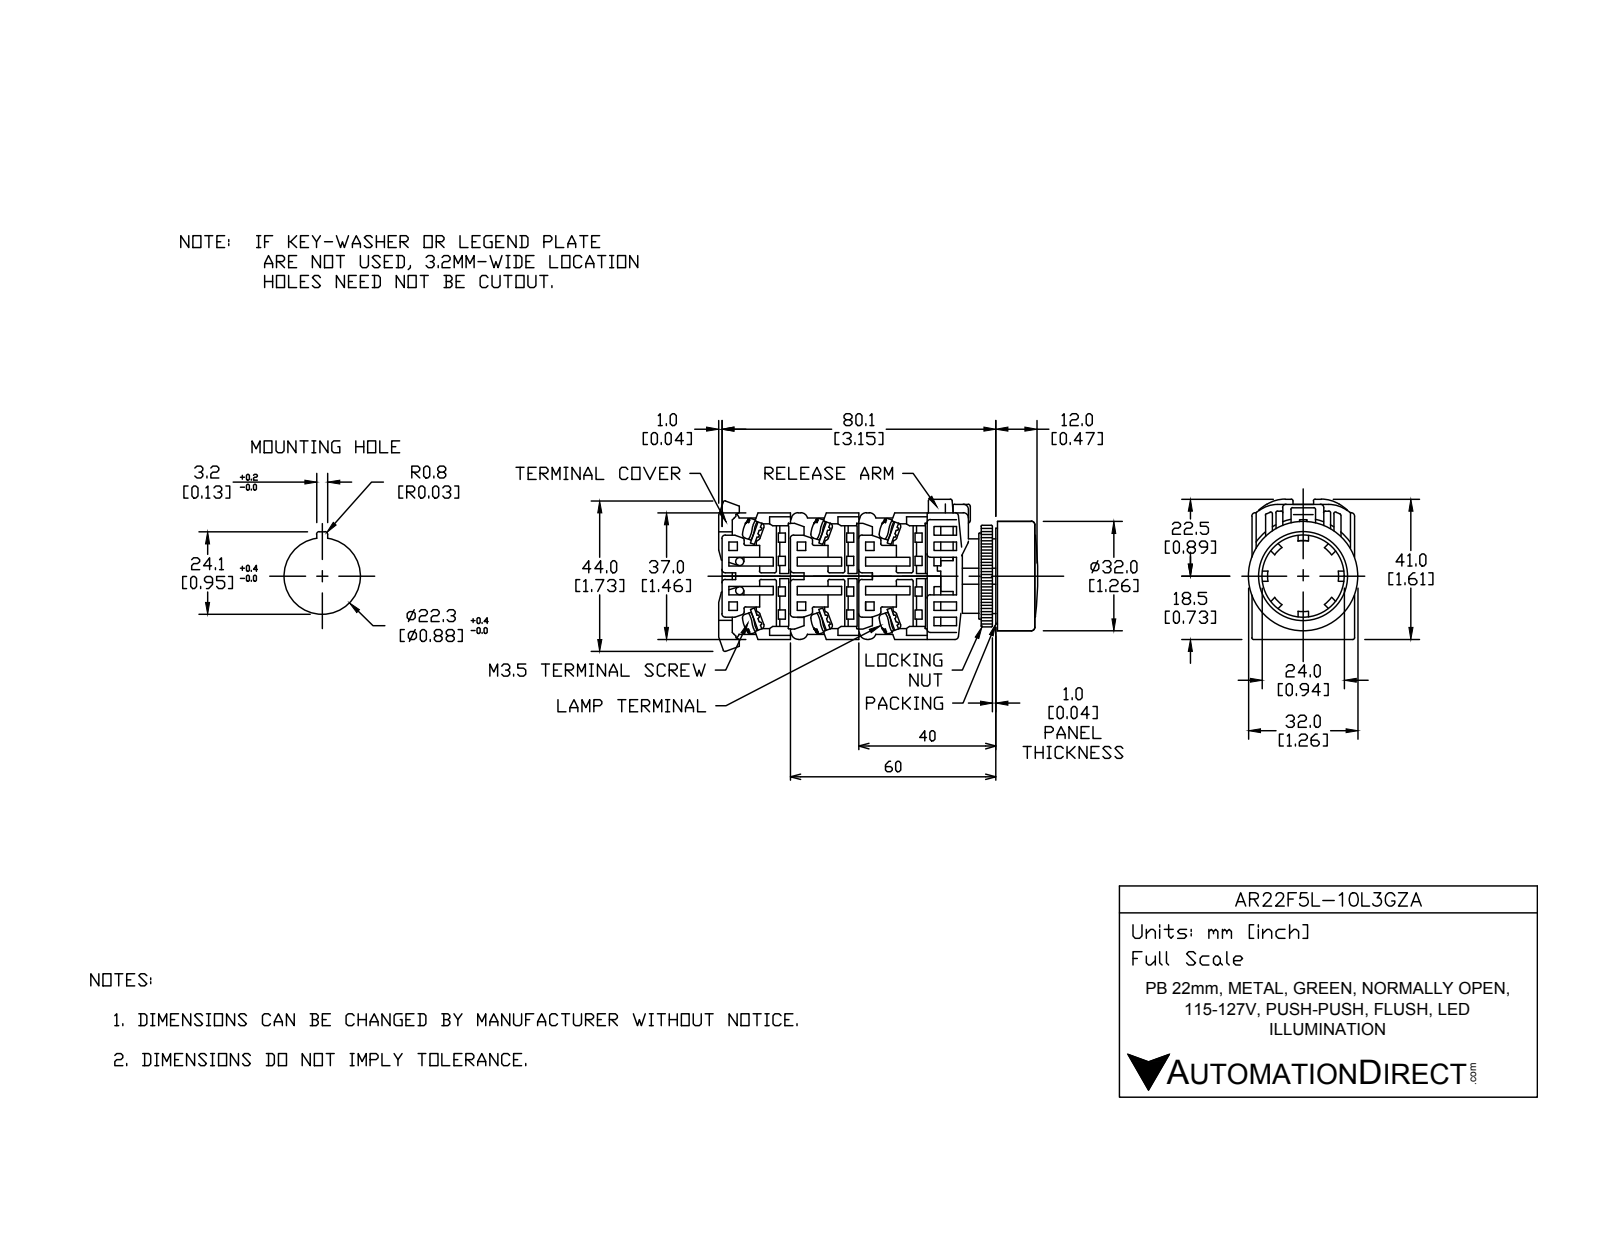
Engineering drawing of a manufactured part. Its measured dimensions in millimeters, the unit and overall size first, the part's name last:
Units: millimetres
Overall size (bounding box): 72.75 × 43.81 × 32
Round holes (diameter × count): ⌀21.8 ×1, ⌀22 ×1, ⌀25 ×1, ⌀31 ×1
Round bosses / shafts (diameter × count): ⌀5 ×4, ⌀32 ×1, ⌀30.5 ×1, ⌀29.8 ×1, ⌀24 ×1, ⌀23.8 ×1, ⌀21.75 ×1, ⌀17 ×1
Partial cylindrical surfaces — rounded edges, fillets, slot ends (radius × count): R0.5 ×32, R1.75 ×8, R5 ×4, R4 ×2, R16.59 ×1, R17.59 ×1
Main face-to-face distances: 1, 18, 29, 20, 28.5, 3, 2, 21, 0.35, 7.5
Volume: 47 521 mm³ · Surface area: 25 721 mm²
Bodies: 16 solids, 451 faces (317 planar, 99 cylindrical, 35 other)
Part name (STEP PRODUCT): AR22F5L-10L3GZA
STEP written by: SolidWorks 2017 (AUTOMOTIVE_DESIGN)
